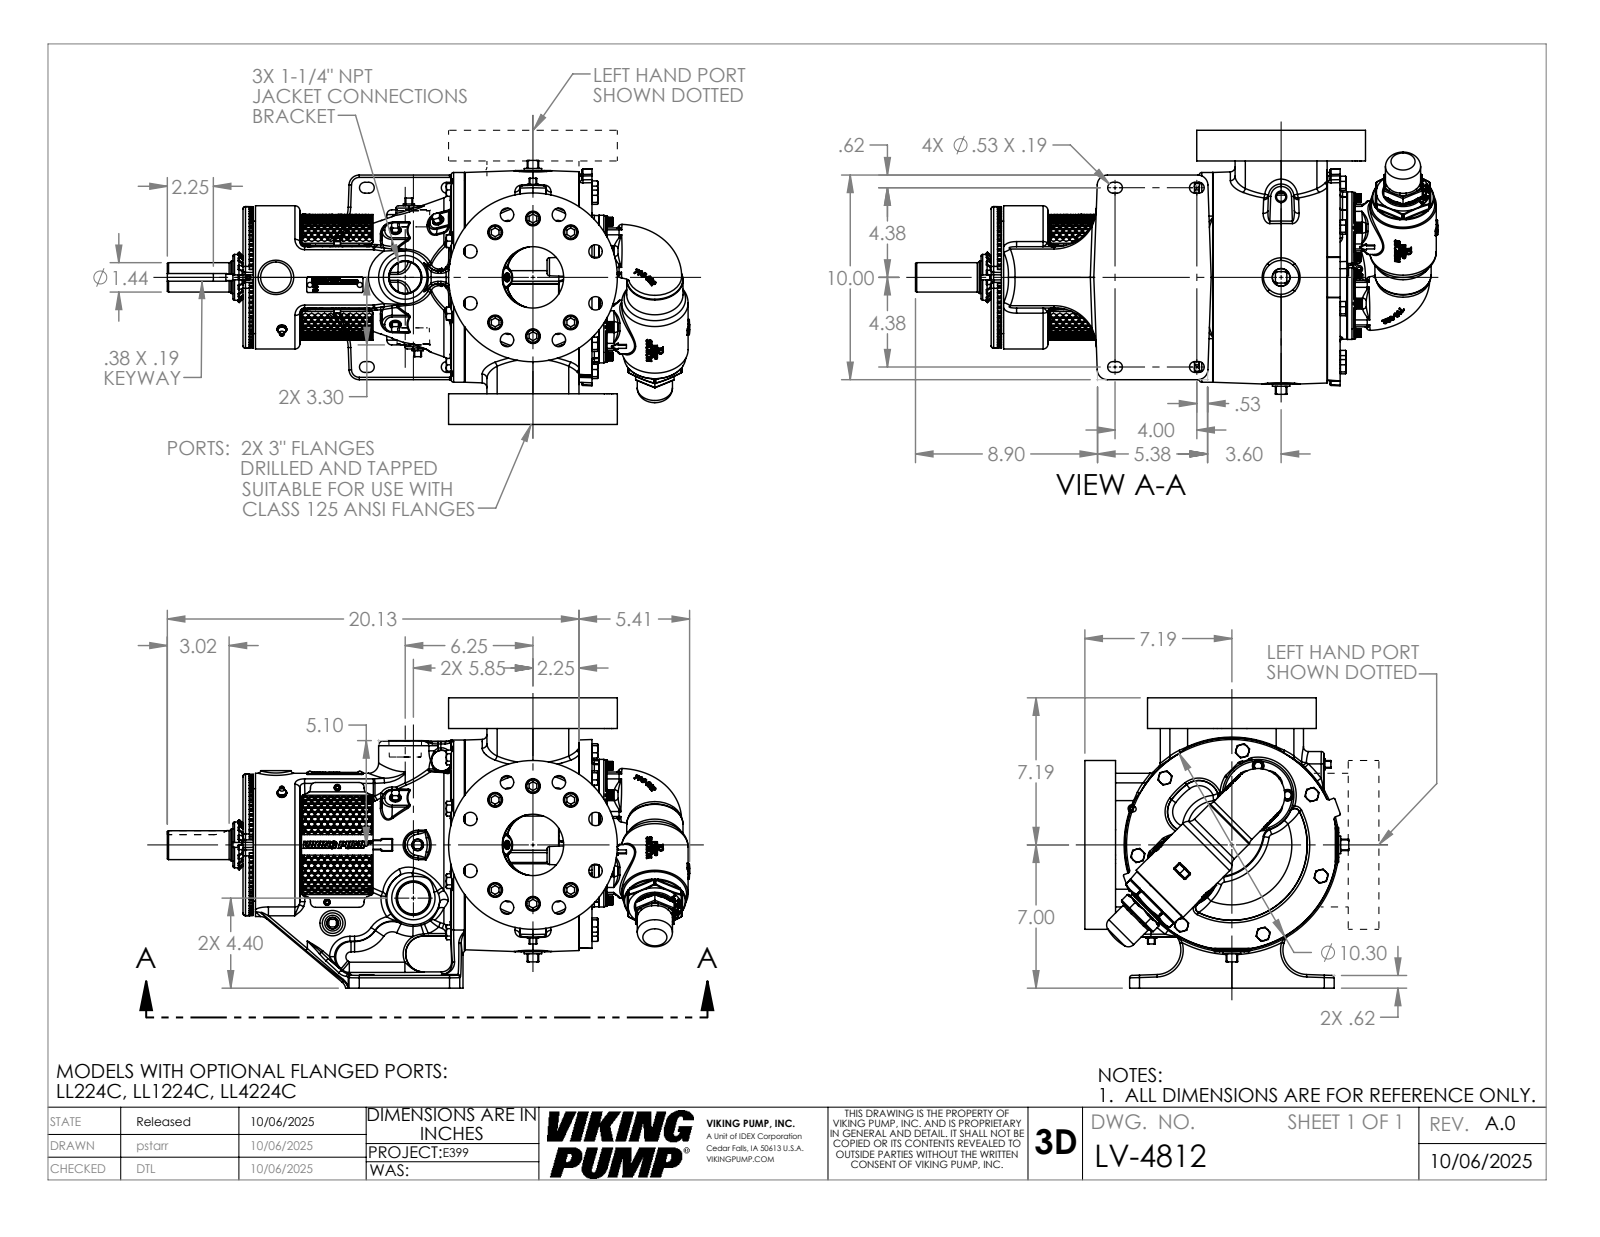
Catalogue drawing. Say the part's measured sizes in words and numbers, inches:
The part is named "LV-4812". Its 3-D file was written by "SolidWorks 2024 (AUTOMOTIVE_DESIGN)". It is 1 solid with 5691 faces: 1932 planar, 1102 cylindrical and 2657 other. Overall it measures 25.533 by 14.188 by 12.903 inches. Its volume is 1 193 cubic inches and its surface area 1 585 square inches. Round holes: 16 of diameter 0.656, 12 of diameter 0.719, 9 of diameter 0.25, 8 of diameter 1.094, 6 of diameter 0.199, 3 of diameter 0.159, 2 of diameter 0.266, 2 of diameter 0.313, 2 of diameter 3, 1 of diameter 0.453, 1 of diameter 1.552, 1 of diameter 1.577. Round bosses or shafts: 12 of diameter 0.66, 10 of diameter 0.625, 8 of diameter 0.563, 5 of diameter 0.625, 3 of diameter 0.312, 3 of diameter 0.19, 2 of diameter 8.25, 2 of diameter 3.5. Partial cylindrical surfaces (rounded edges, fillets, slot ends): 109 of radius 0.063, 74 of radius 0.069, 60 of radius 0.12, 36 of radius 0.03, 26 of radius 0.5, 16 of radius 0.24, 16 of radius 0.45, 12 of radius 0.06. The main face-to-face distances are 1.5, 14.187, 12.687, 10.77, 3.54, 14.31, 0.5, 2.25, 1.382, 0.118. The hole center spacings are 3.313, 4.685, 3, 2.535, 2.875, 1.375, 1.036, 1.281.
